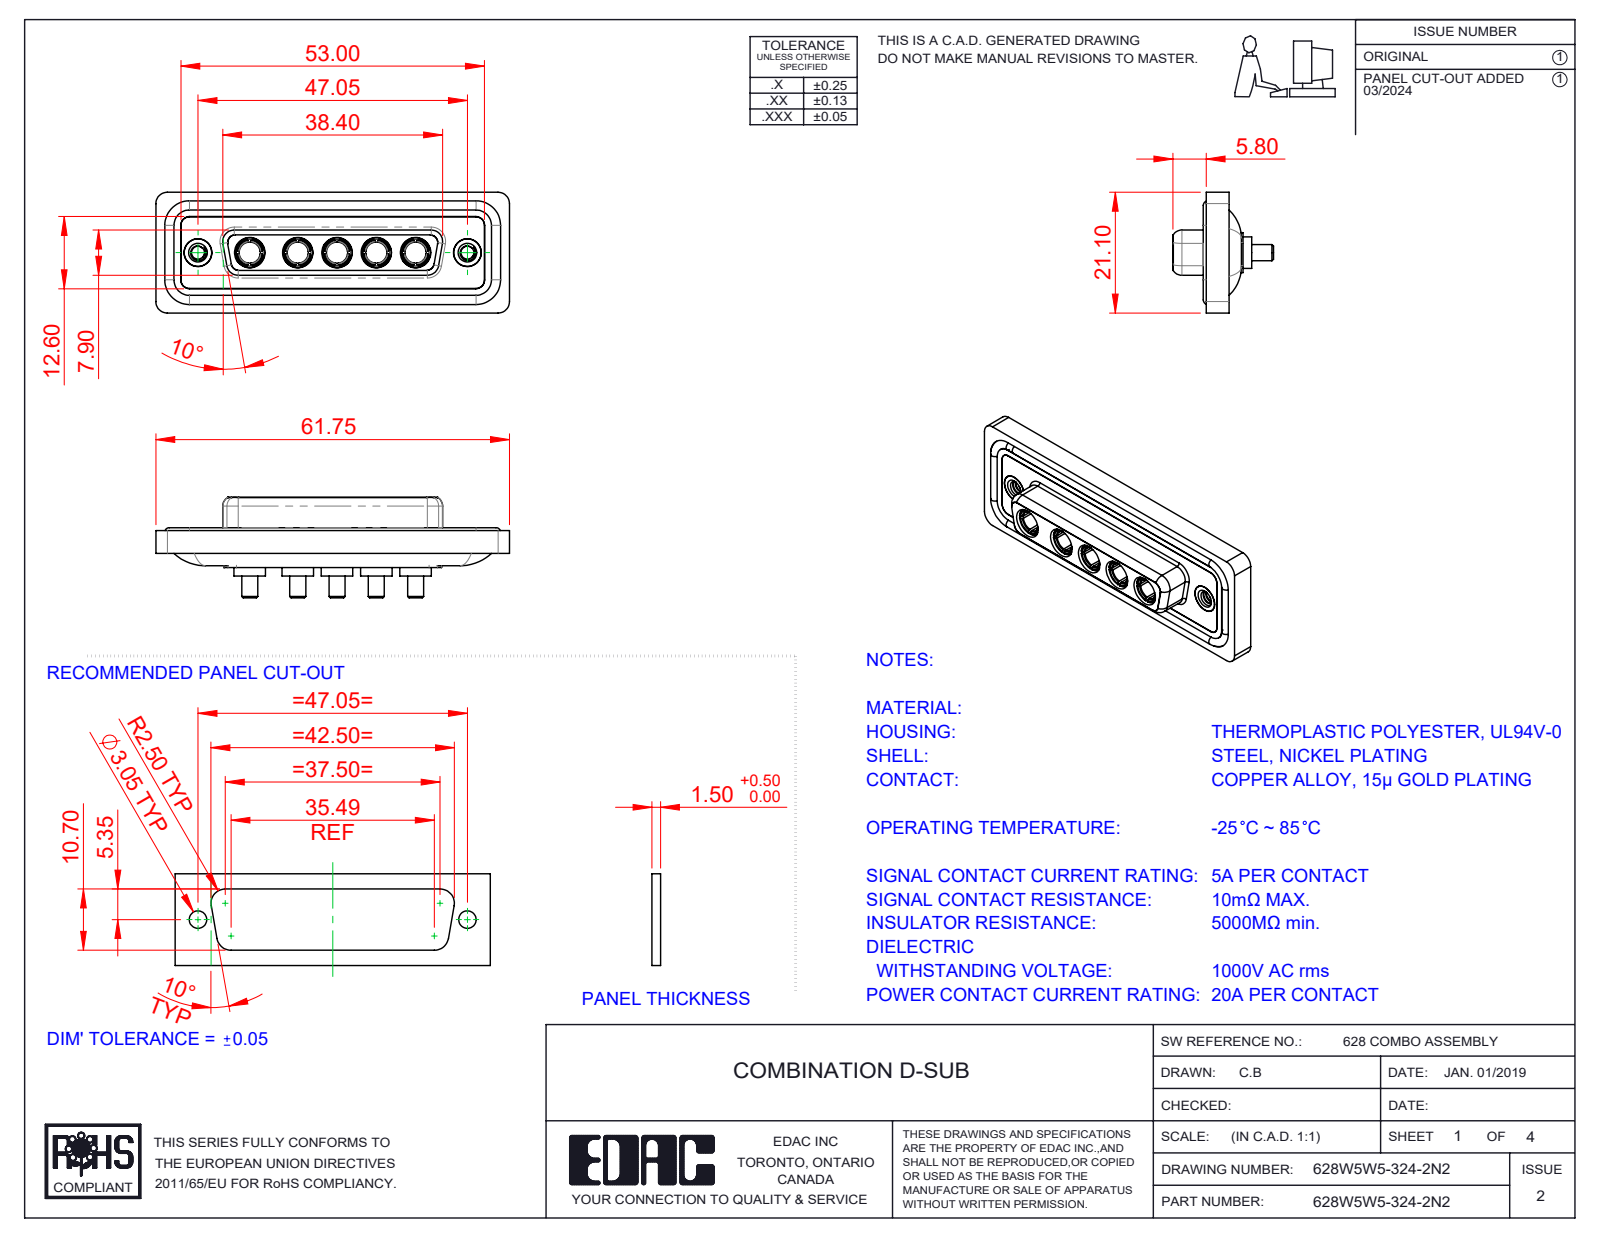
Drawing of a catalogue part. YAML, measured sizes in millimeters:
part_name: "628Combo Waterproof Housing_25 Contacts; 628Combo Shell Front_25 Contacts; Power Socket_20A S; 628Combo Threaded Rivet_2 (+3 more)"
step_written_by: "SolidWorks 2023 (CONFIG_CONTROL_DESIGN)"
units: millimeters
bodies: {solids: 17, faces: 756, planar: 250, cylindrical: 303, other: 203}
overall_size: [61.75, 21.1, 17.55]
volume: 8172
surface_area: 13415
round_holes:
  - {diameter: 4.85, count: 7}
  - {diameter: 3.7, count: 5}
  - {diameter: 5.3, count: 5}
  - {diameter: 2.26, count: 2}
  - {diameter: 4, count: 2}
  - {diameter: 4.05, count: 2}
  - {diameter: 5, count: 2}
round_bosses_or_shafts:
  - {diameter: 5.5, count: 5}
  - {diameter: 5.2, count: 5}
  - {diameter: 4.96, count: 5}
  - {diameter: 4.75, count: 5}
  - {diameter: 3.75, count: 5}
  - {diameter: 2.8, count: 5}
  - {diameter: 1.6, count: 4}
  - {diameter: 4.95, count: 2}
partial_cylinders:
  - {radius: 1.5, count: 22}
  - {radius: 2, count: 18}
  - {radius: 1.35, count: 8}
  - {radius: 1.6, count: 8}
  - {radius: 2.1, count: 5}
  - {radius: 0.25, count: 4}
  - {radius: 0.5, count: 4}
  - {radius: 0.6, count: 4}
face_to_face_distances: [0.4, 1.8, 7.45, 5.65, 0.5, 7.05, 6.6, 1.6, 1.1, 2.9]
hole_center_spacings: [6.86, 9.04, 13.72, 38.01, 8.39, 15.25, 15.9, 17.43]
